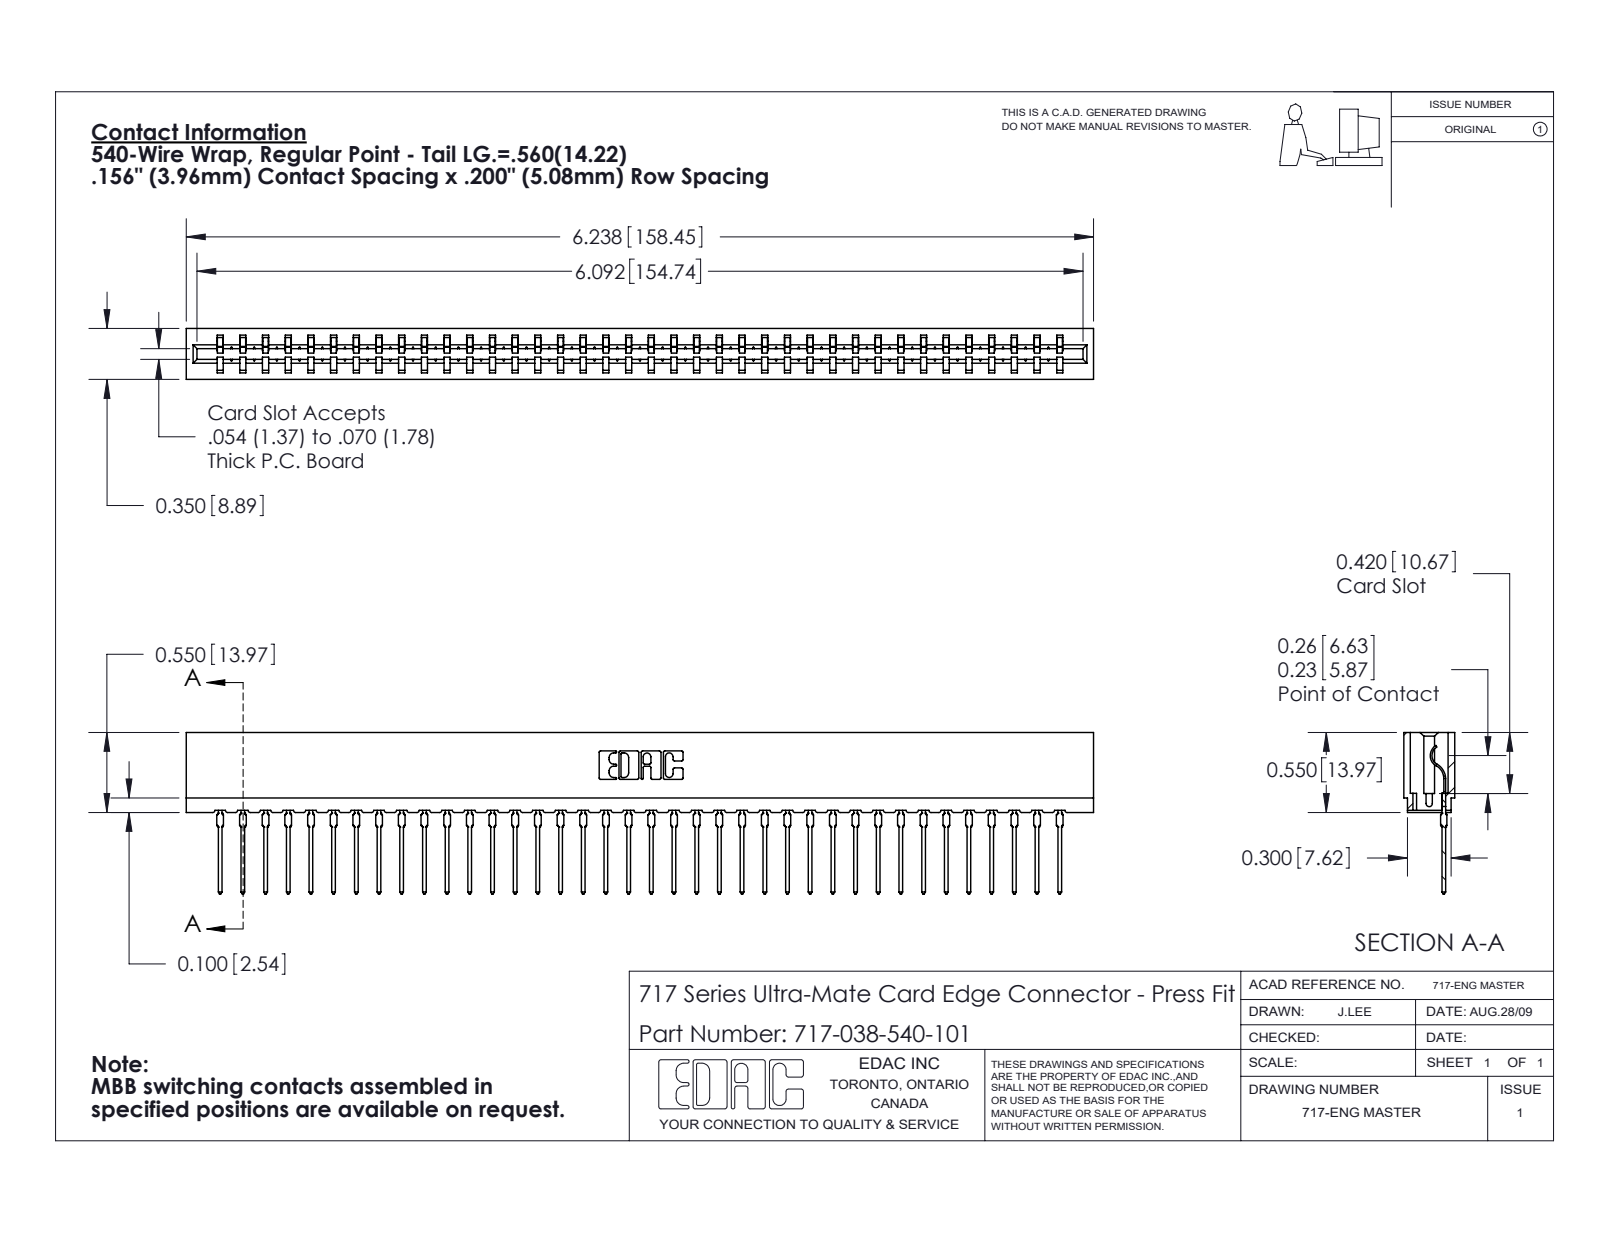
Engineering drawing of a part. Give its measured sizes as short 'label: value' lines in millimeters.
name: 717 Part_Insulator Option - 06; 745-292-001_540; 717-038-540-101
written by: SolidWorks 2020 (CONFIG_CONTROL_DESIGN)
unit: mm
bodies: 39 solids, 4388 faces (2638 planar, 762 cylindrical, 988 other)
size: 158.4 × 28.2 × 8.9
volume: 13 500 mm³; area: 19 340 mm²
rounds: 76× R0.4, 76× R0.5, 22× R0.3, 6× R0.2, 6× R0.8, 4× R0.1, 4× R0.3, 3× R0.7
face distances: 5.4, 3.5, 8.9, 1.9, 1.6, 7.3, 1.9, 3.8, 1.1, 7.7
